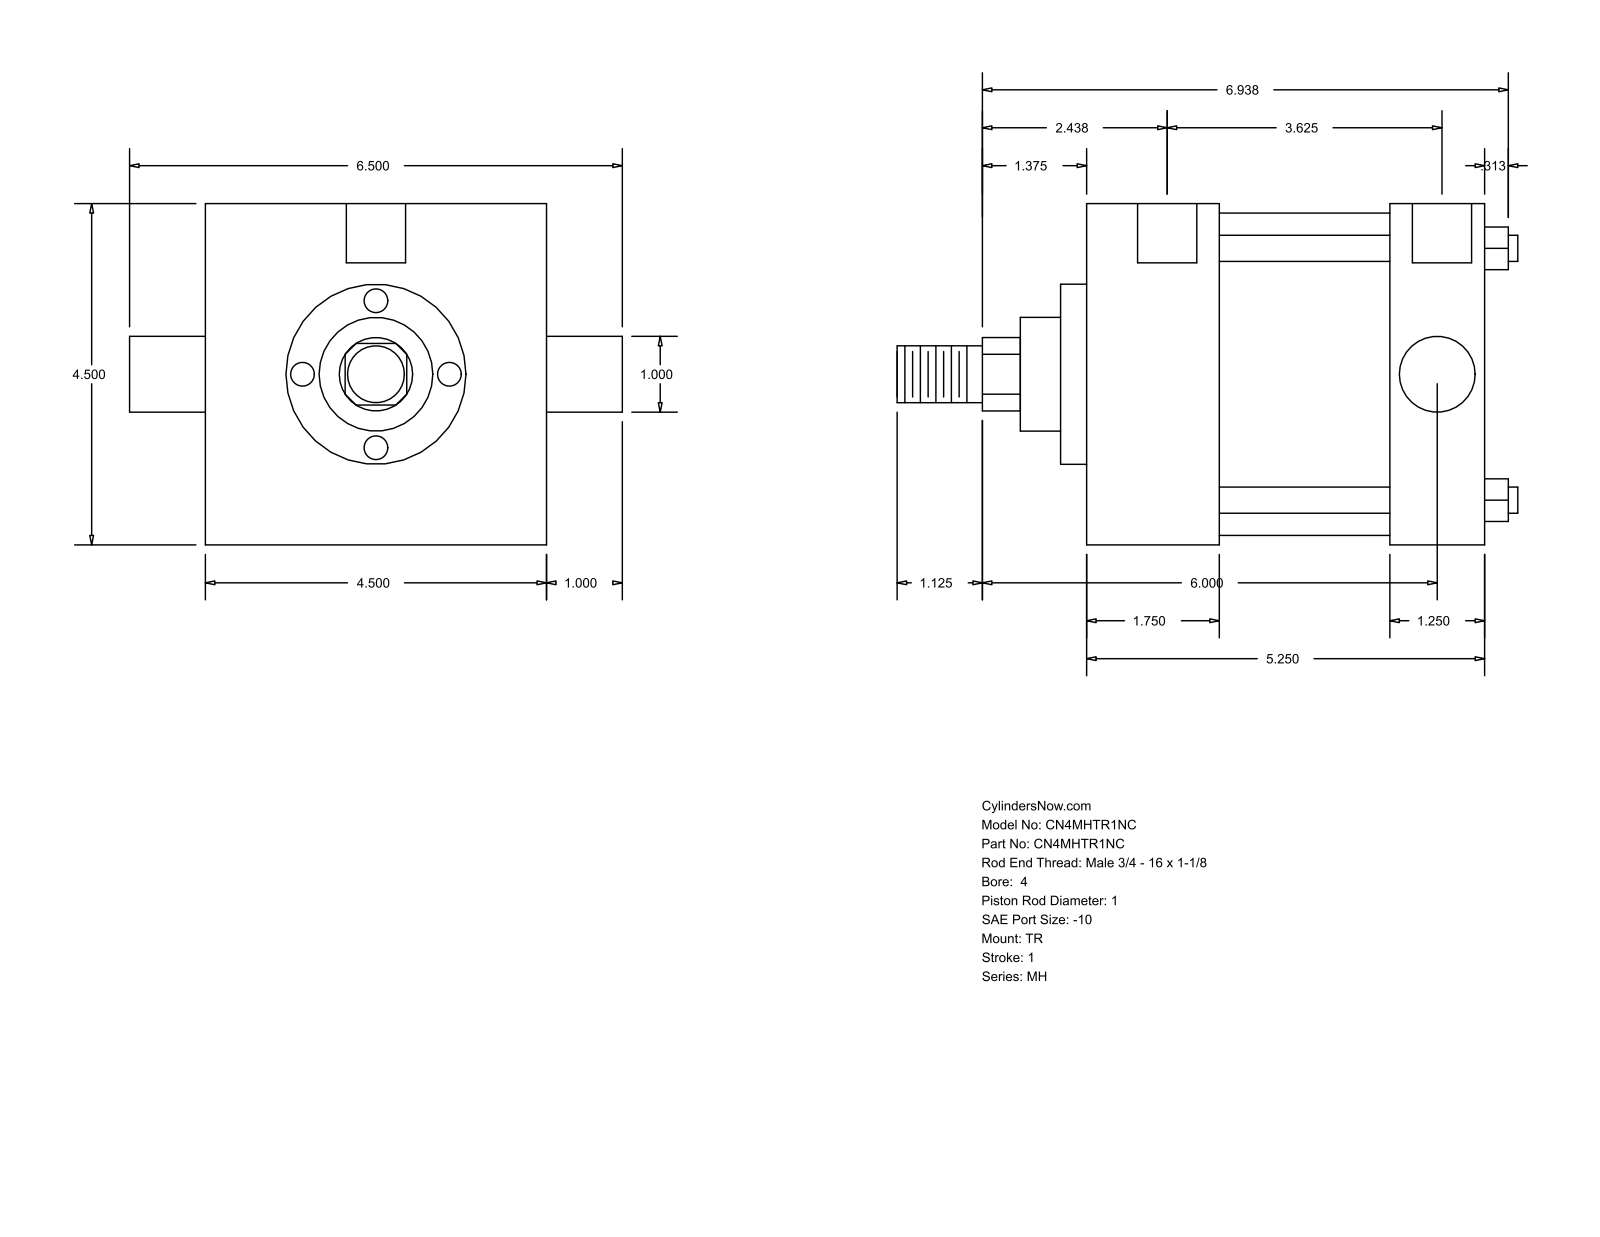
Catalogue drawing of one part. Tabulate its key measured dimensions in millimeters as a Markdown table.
| quantity | value |
| --- | --- |
| part name | MH_TR__0400_1 |
| STEP written by | GSSL Pune (CONFIG_CONTROL_DESIGN) |
| units | millimeters |
| bodies | 0 solids, 86 faces (61 planar, 25 cylindrical, 0 other) |
| overall size | 207.96 × 165.1 × 114.3 |
| round holes (diameter × count) | 8.73 × 3, 19.84 × 2 |
| round bosses / shafts (diameter × count) | 8.76 × 4, 25.4 × 2, 107.95 × 1, 60.33 × 1, 38.1 × 1, 19.05 × 1 |
| partial cylindrical surfaces (radius × count) | 12.29 × 1 |
| main face-to-face distances | 114.3, 133.36, 44.46, 88.9, 101.61, 57.15, 31.75, 8.73, 53.19, 110.34 |
| hole center spacings | 1.58, 93.66, 92.08, 95.24 |
